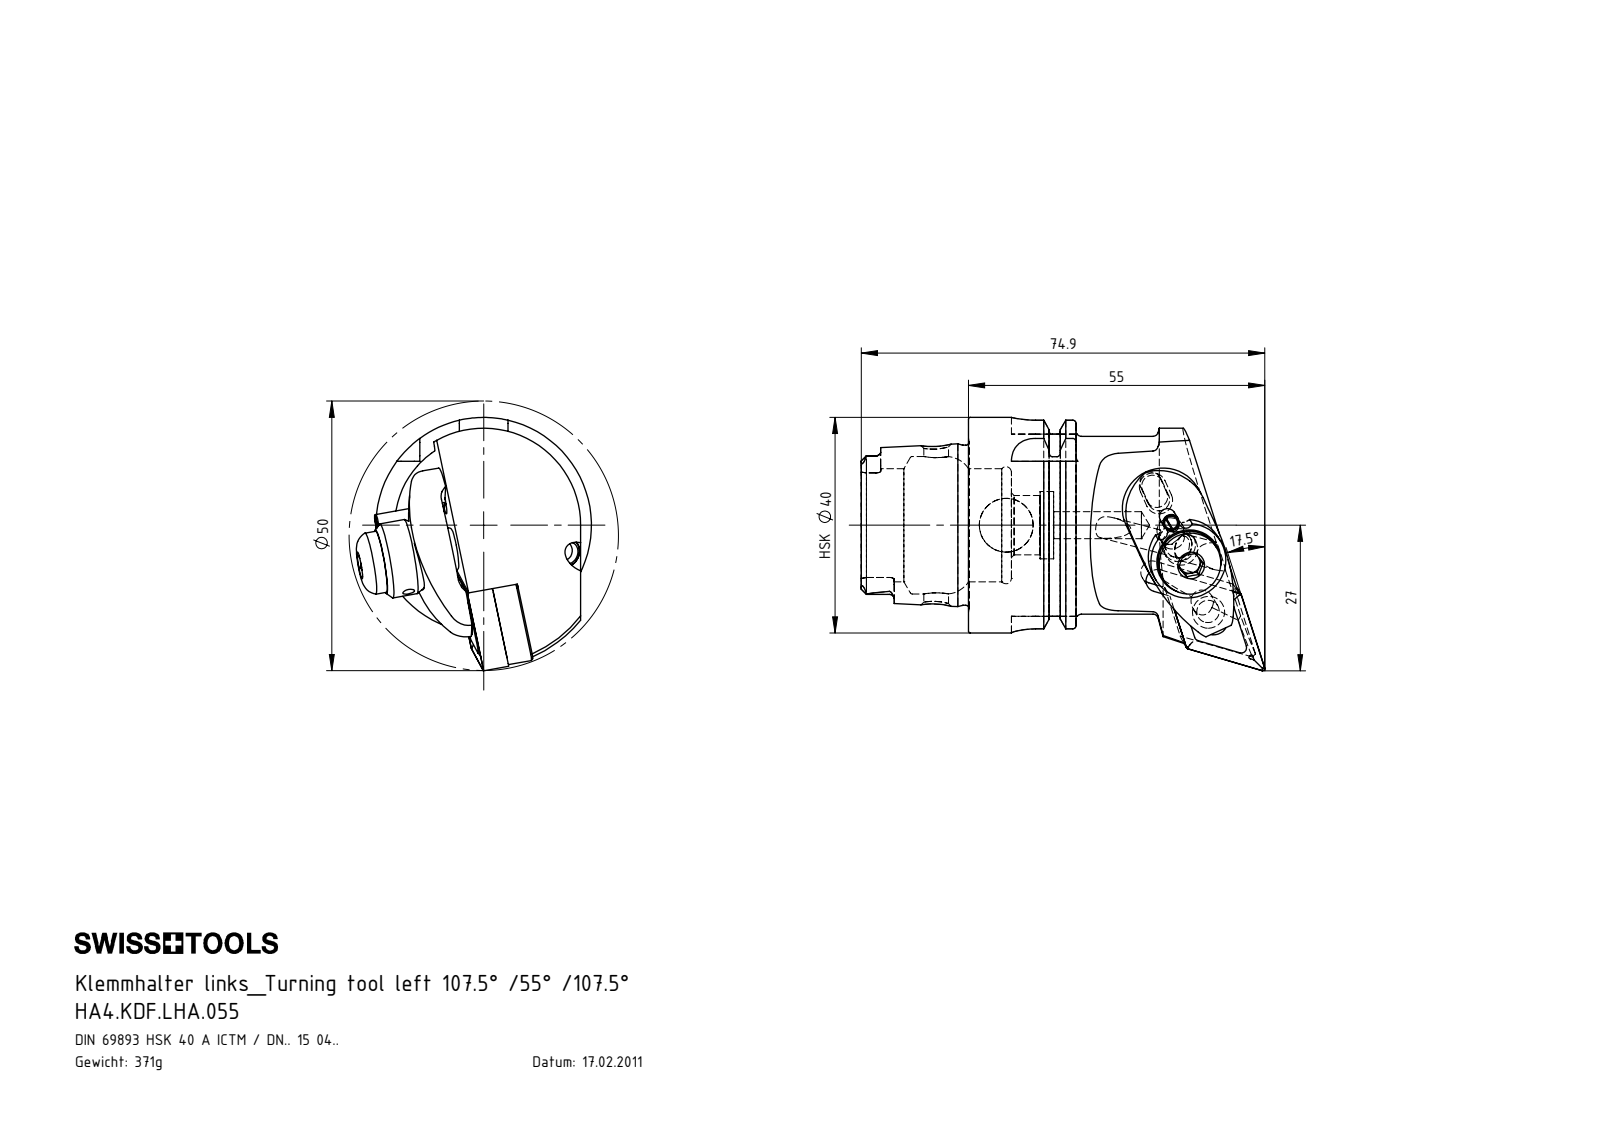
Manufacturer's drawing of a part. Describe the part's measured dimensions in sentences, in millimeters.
The part is named "WCC-ER5.102.005_A; HA4-KDF.LHA.055_A_Fertigbearbeitung; WCC-ER4.103.032_A; HA4.KDF.LHA.055 (+7 more)". Its 3-D file was written by "SolidWorks 2022 (AUTOMOTIVE_DESIGN)". It is 11 solids with 465 faces: 122 planar, 154 cylindrical and 189 other. Overall it measures 74.9 by 47 by 43.63 millimeters. Its volume is 46 482 cubic millimeters and its surface area 19 019 square millimeters. Round holes: 3 of diameter 2, 3 of diameter 5, 2 of diameter 4.2, 2 of diameter 7, 1 of diameter 2.4, 1 of diameter 3, 1 of diameter 4, 1 of diameter 4.6, 1 of diameter 5.16, 1 of diameter 6.2, 1 of diameter 6.5, 1 of diameter 8.5. Round bosses or shafts: 2 of diameter 5, 2 of diameter 3, 1 of diameter 40, 1 of diameter 34.75, 1 of diameter 33, 1 of diameter 29.71, 1 of diameter 14, 1 of diameter 11.5. Partial cylindrical surfaces (rounded edges, fillets, slot ends): 6 of radius 0.39, 6 of radius 0.69, 6 of radius 0.9, 4 of radius 0.4, 4 of radius 4.5, 3 of radius 1.5, 3 of radius 3, 2 of radius 1.82. The main face-to-face distances are 6.02, 12.7, 12.3, 7.95, 7.34, 1.32, 19.95, 12, 10.5, 3.16. The hole center spacings are 23, 14.81, 15.02, 23.01, 7.96, 7.98, 7.99, 8.
